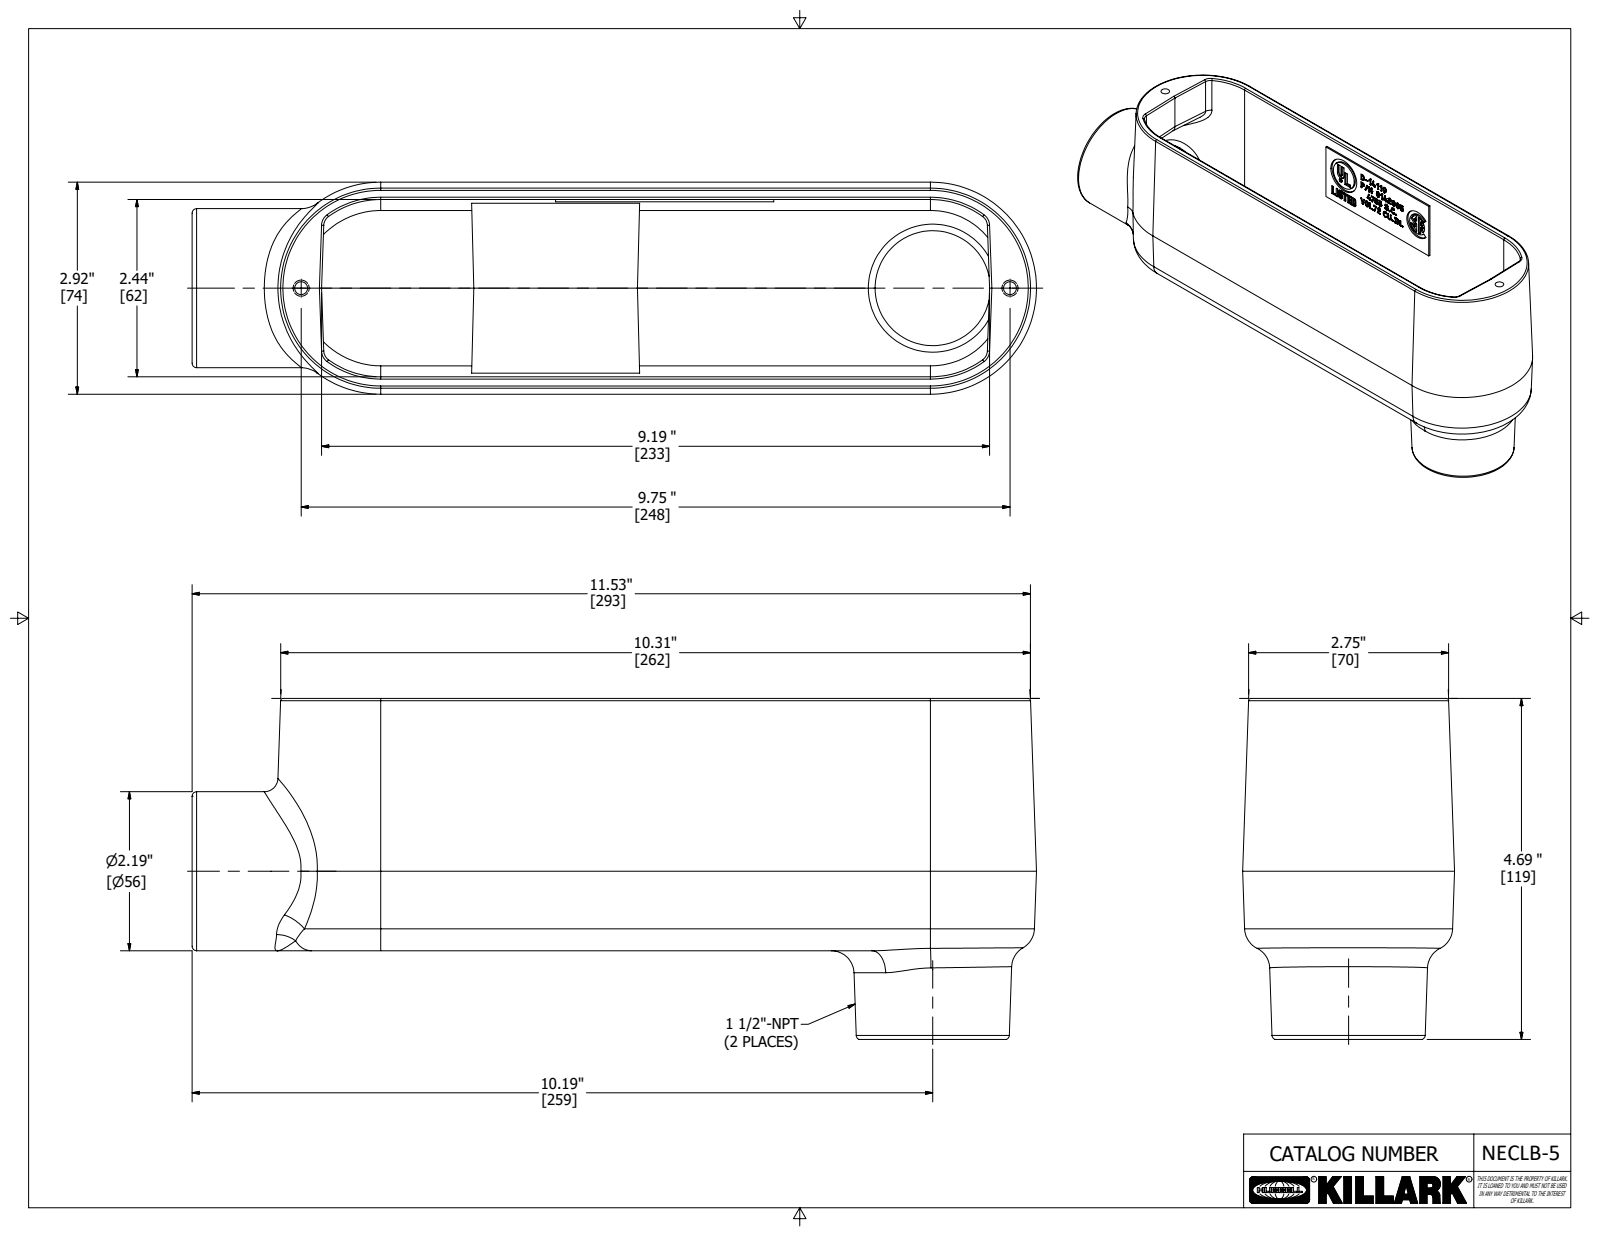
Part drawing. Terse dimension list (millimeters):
name: 0142005-2
written by: Autodesk Inventor 2020 (AP242_MANAGED_MODEL_BASED_3D_ENGINEERING_MIM_LF)
unit: mm
bodies: 1 solid, 1037 faces (456 planar, 23 cylindrical, 558 other)
size: 295 × 119.1 × 74.1
volume: 397 200 mm³; area: 150 300 mm²
holes: 2× ⌀4.5
bosses: 1× ⌀55.5
rounds: 8× R0.8, 4× R4, 4× R4.7, 2× R8, 2× R31
face distances: 61.9, 74, 0.9, 88.1, 0.8, 61.1, 0.8, 87.3, 233.1, 233.1
hole spacings: 247.7
